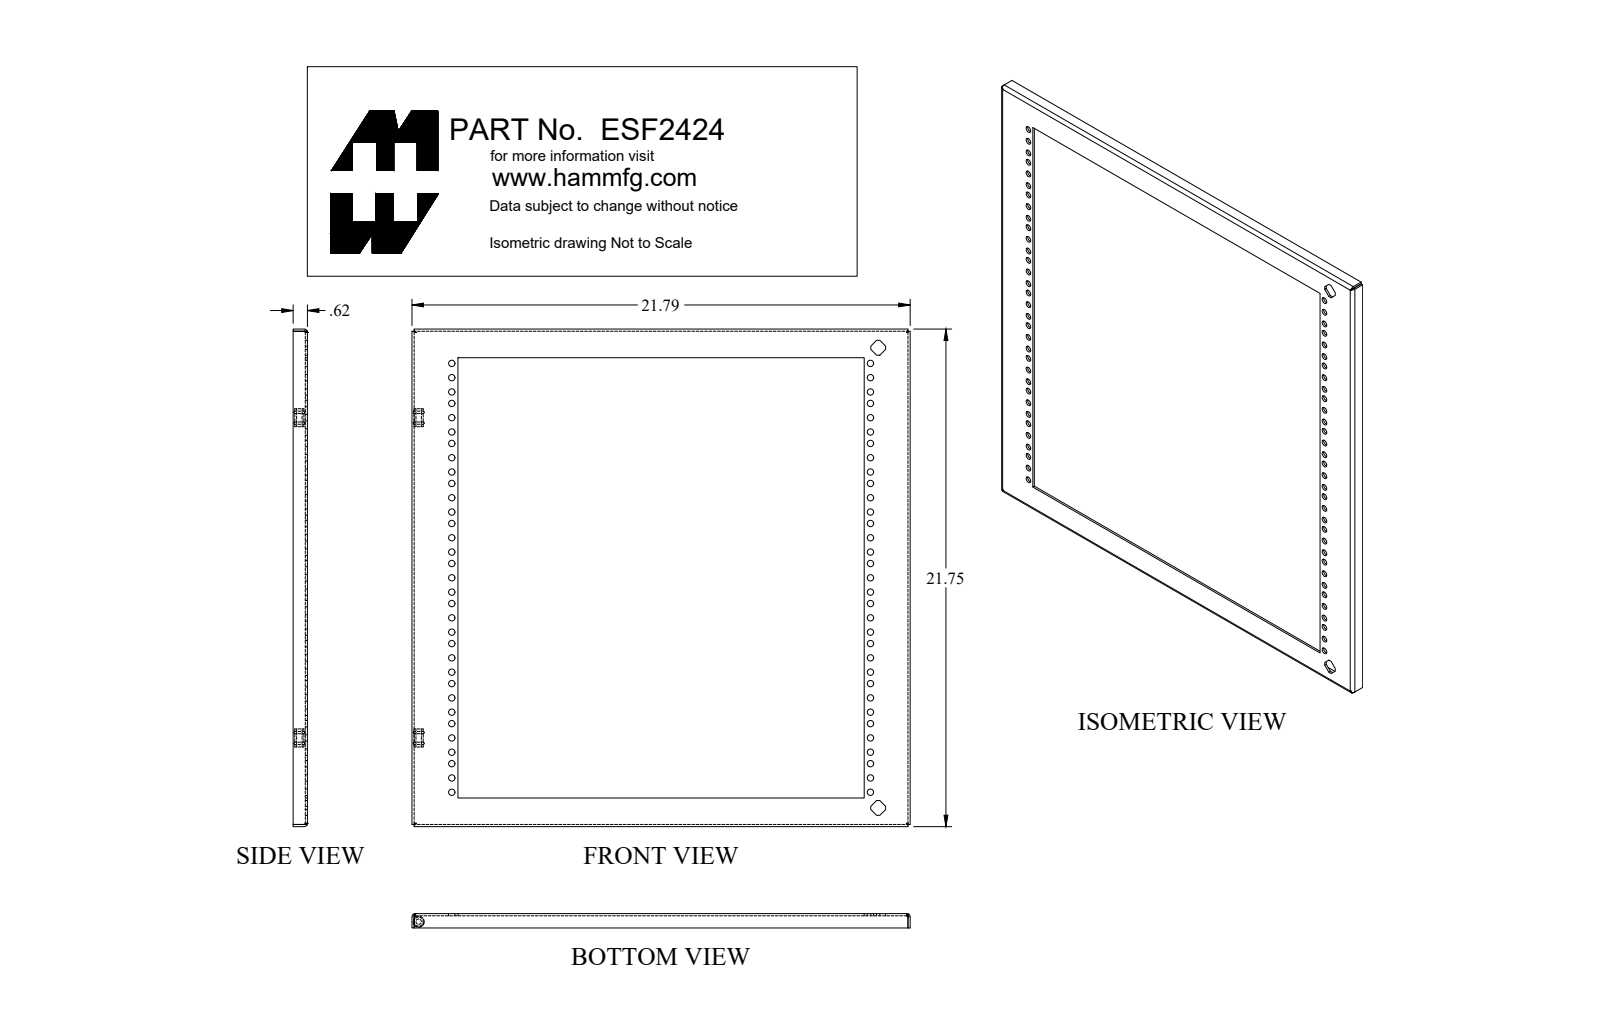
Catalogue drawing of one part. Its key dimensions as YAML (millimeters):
part_name: "ESF2424"
step_written_by: "SolidWorks 2018 (AUTOMOTIVE_DESIGN)"
units: millimeters
bodies: {solids: 19, faces: 776, planar: 378, cylindrical: 330, other: 68}
overall_size: [602.1, 552.5, 207.3]
volume: 493400
surface_area: 521700
round_holes:
  - {diameter: 7.1, count: 66}
  - {diameter: 3.5, count: 2}
  - {diameter: 4.8, count: 2}
  - {diameter: 6.1, count: 2}
  - {diameter: 13.1, count: 2}
  - {diameter: 6.1, count: 1}
round_bosses_or_shafts:
  - {diameter: 20, count: 2}
  - {diameter: 12.6, count: 2}
  - {diameter: 11, count: 2}
  - {diameter: 9, count: 2}
  - {diameter: 7.1, count: 2}
  - {diameter: 5.7, count: 2}
  - {diameter: 13.6, count: 1}
  - {diameter: 13.6, count: 1}
partial_cylinders:
  - {radius: 1.2, count: 28}
  - {radius: 0.3, count: 24}
  - {radius: 0.9, count: 6}
  - {radius: 2.7, count: 6}
  - {radius: 1.5, count: 4}
  - {radius: 3.6, count: 4}
  - {radius: 3.9, count: 4}
  - {radius: 4, count: 4}
face_to_face_distances: [2.4, 1.8, 559, 1.8, 1, 560.8, 19.8, 22.2, 21.6, 24.1]
hole_center_spacings: [44.5, 88.9, 133.4, 177.8, 222.3, 266.7, 12.7, 15.9]
